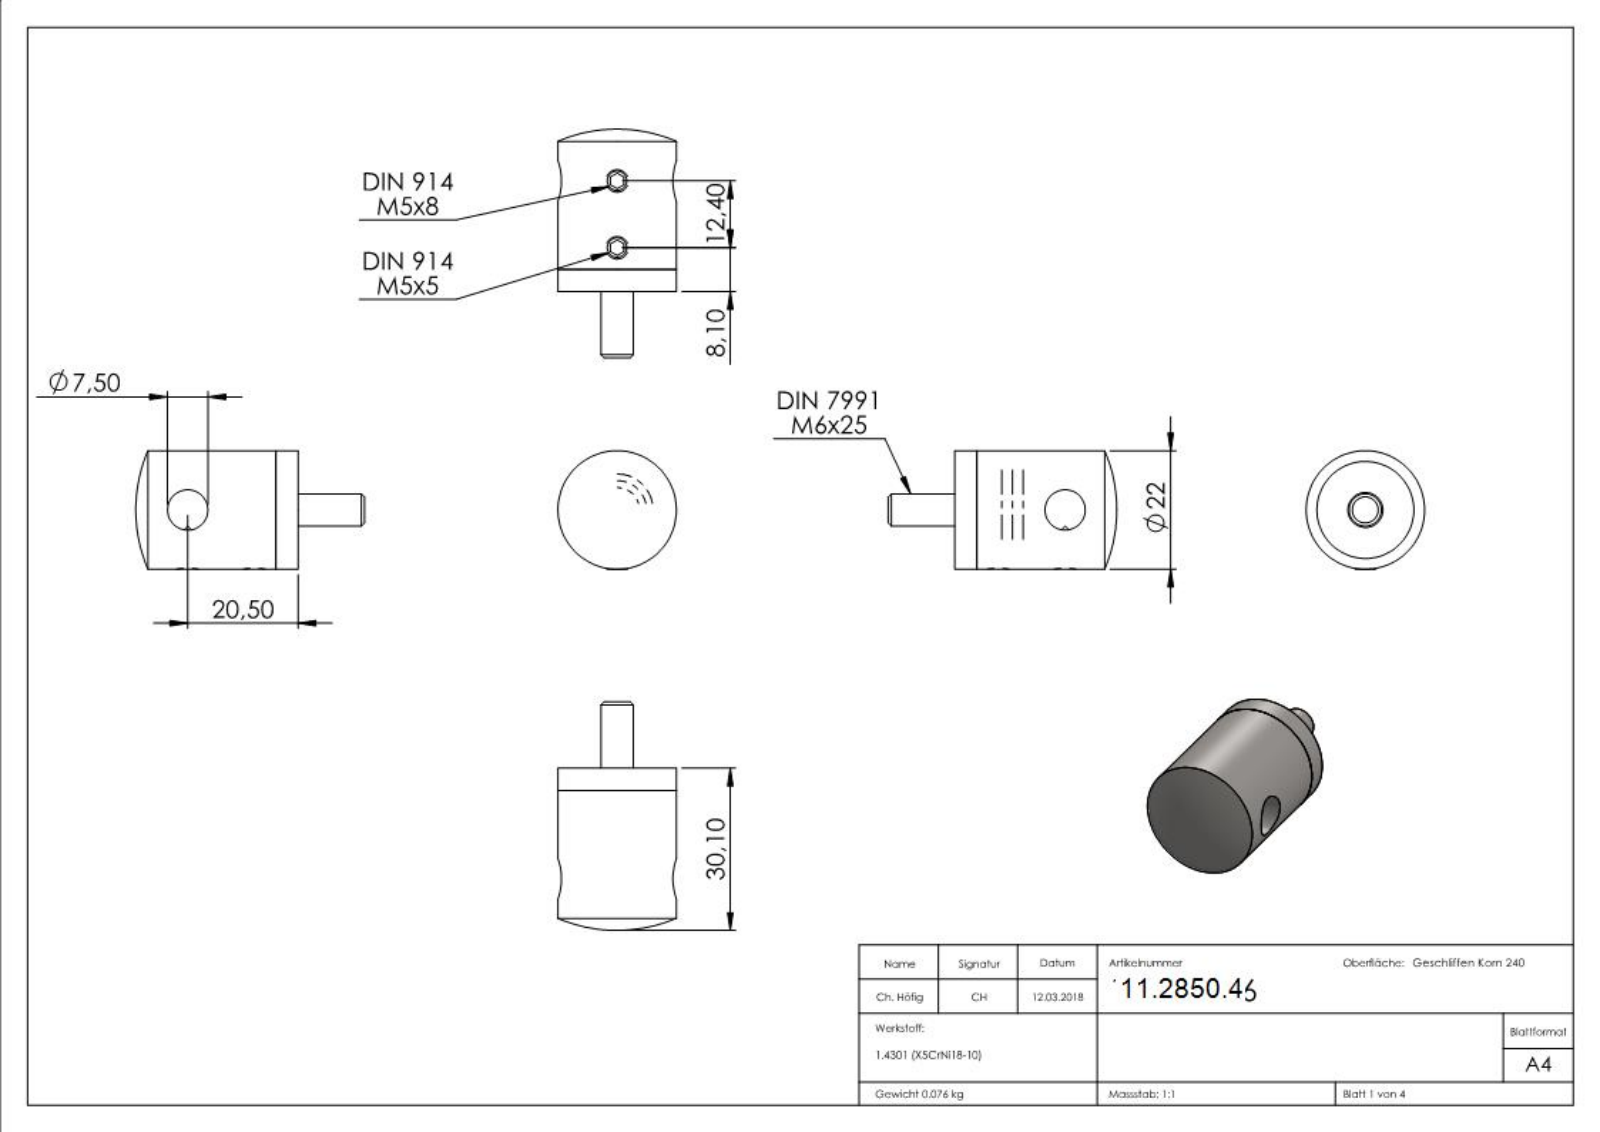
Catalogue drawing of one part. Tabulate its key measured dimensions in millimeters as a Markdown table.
| quantity | value |
| --- | --- |
| part name | 10002X00X Teil1; DIN914; 10002X00X Teil2_10002300X Teil2; 100023006 (+6 more) |
| STEP written by | SolidWorks 2018 (CONFIG_CONTROL_DESIGN) |
| units | millimeters |
| bodies | 5 solids, 283 faces (133 planar, 14 cylindrical, 136 other) |
| overall size | 42.45 × 24 × 22 |
| volume | 9 534 mm³ |
| surface area | 5 780 mm² |
| round holes (diameter × count) | 4.2 × 2, 6.5 × 1, 7.5 × 1, 12.1 × 1, 18 × 1 |
| round bosses / shafts (diameter × count) | 5 × 2, 22 × 1, 12 × 1, 6 × 1 |
| main face-to-face distances | 2, 2.1, 4.1, 12.65, 10.55, 8.55, 4, 12.35, 14.45, 16.45 |
| hole center spacings | 12.4 |
